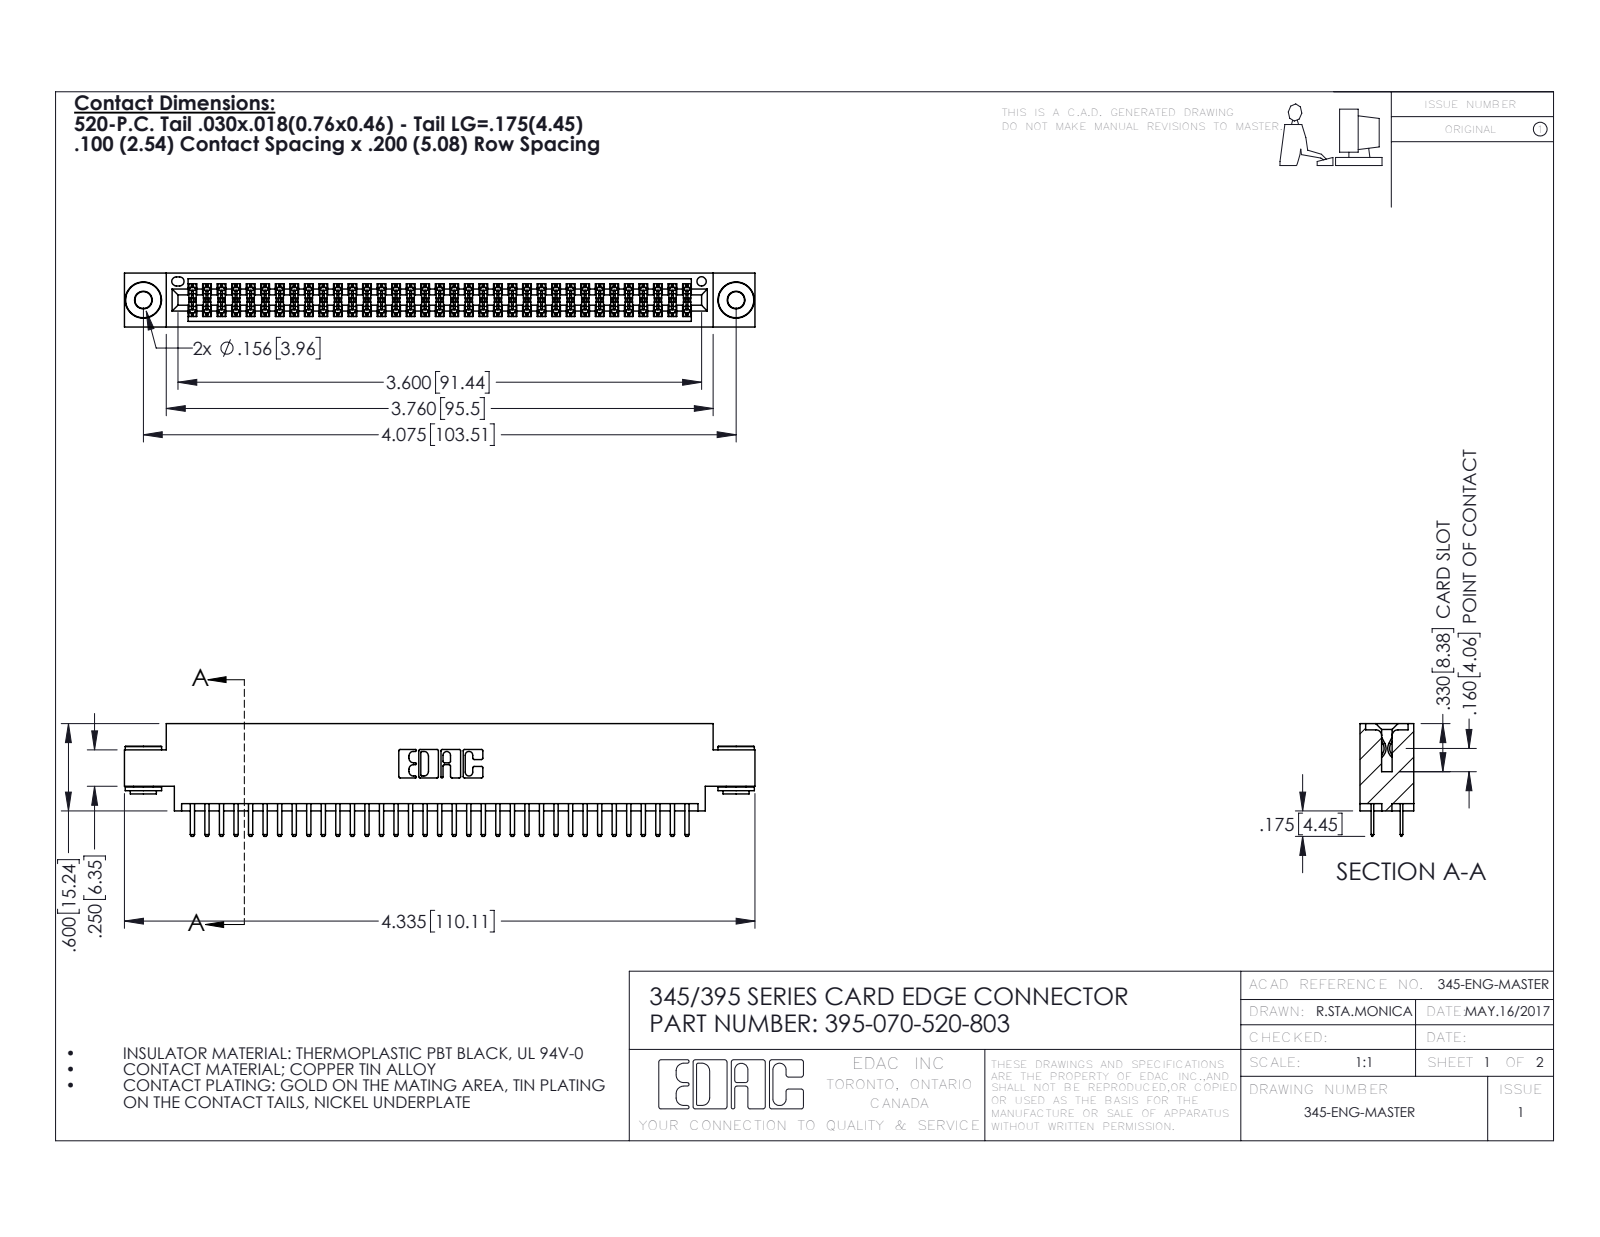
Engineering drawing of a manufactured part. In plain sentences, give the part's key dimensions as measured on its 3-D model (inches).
The part is named "345-250-002_345-250-002-102; 345 Part_0.170 Offset - 0.156 Dia-TH; 395-070-520-803; 345-292-001_345-293-120". Its 3-D file was written by "SolidWorks 2016 (CONFIG_CONTROL_DESIGN)". It is 73 solids with 3948 faces: 2544 planar, 1396 cylindrical and 8 other. Overall it measures 4.335 by 0.775 by 0.37 inches. Its volume is 0.641 cubic inches and its surface area 24.3 square inches. Round holes: 2 of diameter 0.116, 2 of diameter 0.156, 1 of diameter 0.064. Round bosses or shafts: 2 of diameter 0.25, 2 of diameter 0.18, 2 of diameter 0.136. Partial cylindrical surfaces (rounded edges, fillets, slot ends): 105 of radius 0.006, 74 of radius 0.01, 22 of radius 0.01, 6 of radius 0.007, 6 of radius 0.031, 3 of radius 0.026, 2 of radius 0.014, 2 of radius 0.019. The main face-to-face distances are 0.072, 0.298, 0.37, 0.2, 0.098, 0.272, 0.025, 0.225, 0.175, 0.022. The hole center spacings are 0.27, 3.839, 4.075.
